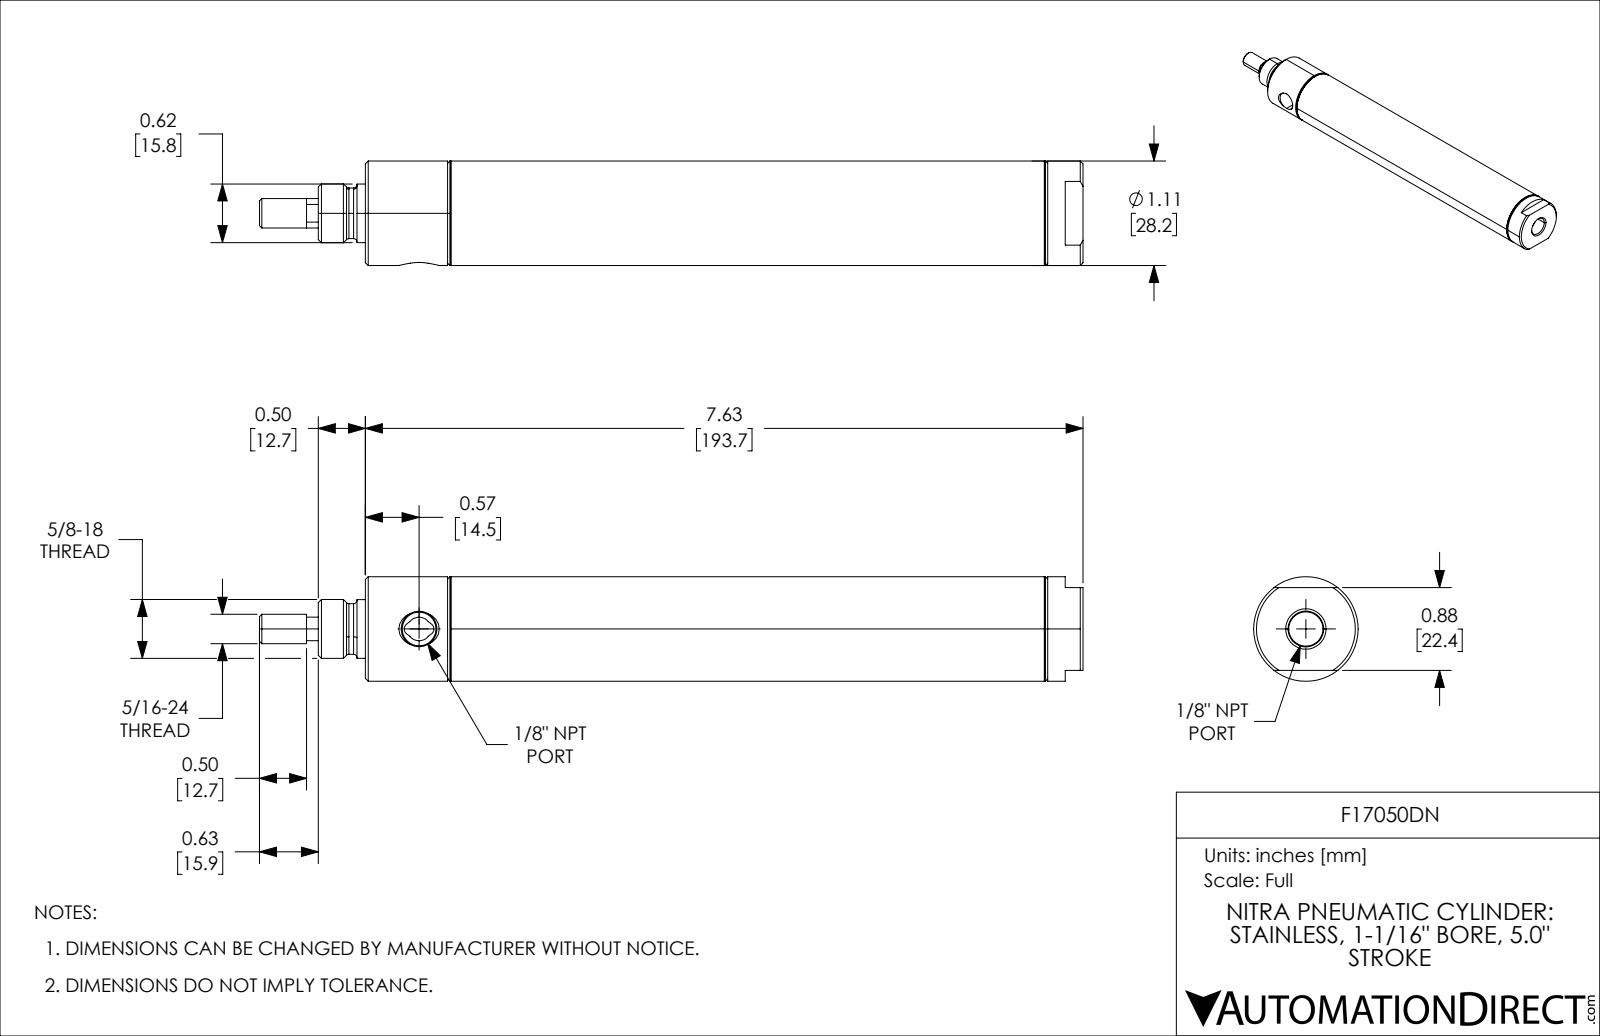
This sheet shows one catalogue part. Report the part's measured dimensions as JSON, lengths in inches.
{"part_name": "F17050DN_5; F17050DN_3; F17050DN_9; F17050DN_7 (+1 more)", "step_written_by": "SolidWorks 2021 (CONFIG_CONTROL_DESIGN)", "units": "inches", "bodies": {"solids": 4, "faces": 125, "planar": 25, "cylindrical": 44, "other": 56}, "overall_size": [8.75, 1.11, 1.11], "volume_in3": 3.19, "surface_area_in2": 69.84, "round_holes": [[0.336, 1], [0.364, 1], [0.75, 1], [1.012, 1]], "round_bosses_or_shafts": [[1.11, 1], [1.072, 1], [0.625, 1], [0.622, 1], [0.539, 1], [0.313, 1], [0.312, 1]], "partial_cylinders_radius": [[0.125, 1]], "face_to_face_distances": [0.875, 5, 5.875, 6.5, 1.5, 0.625, 1.125, 6.125, 7, 7.625]}
